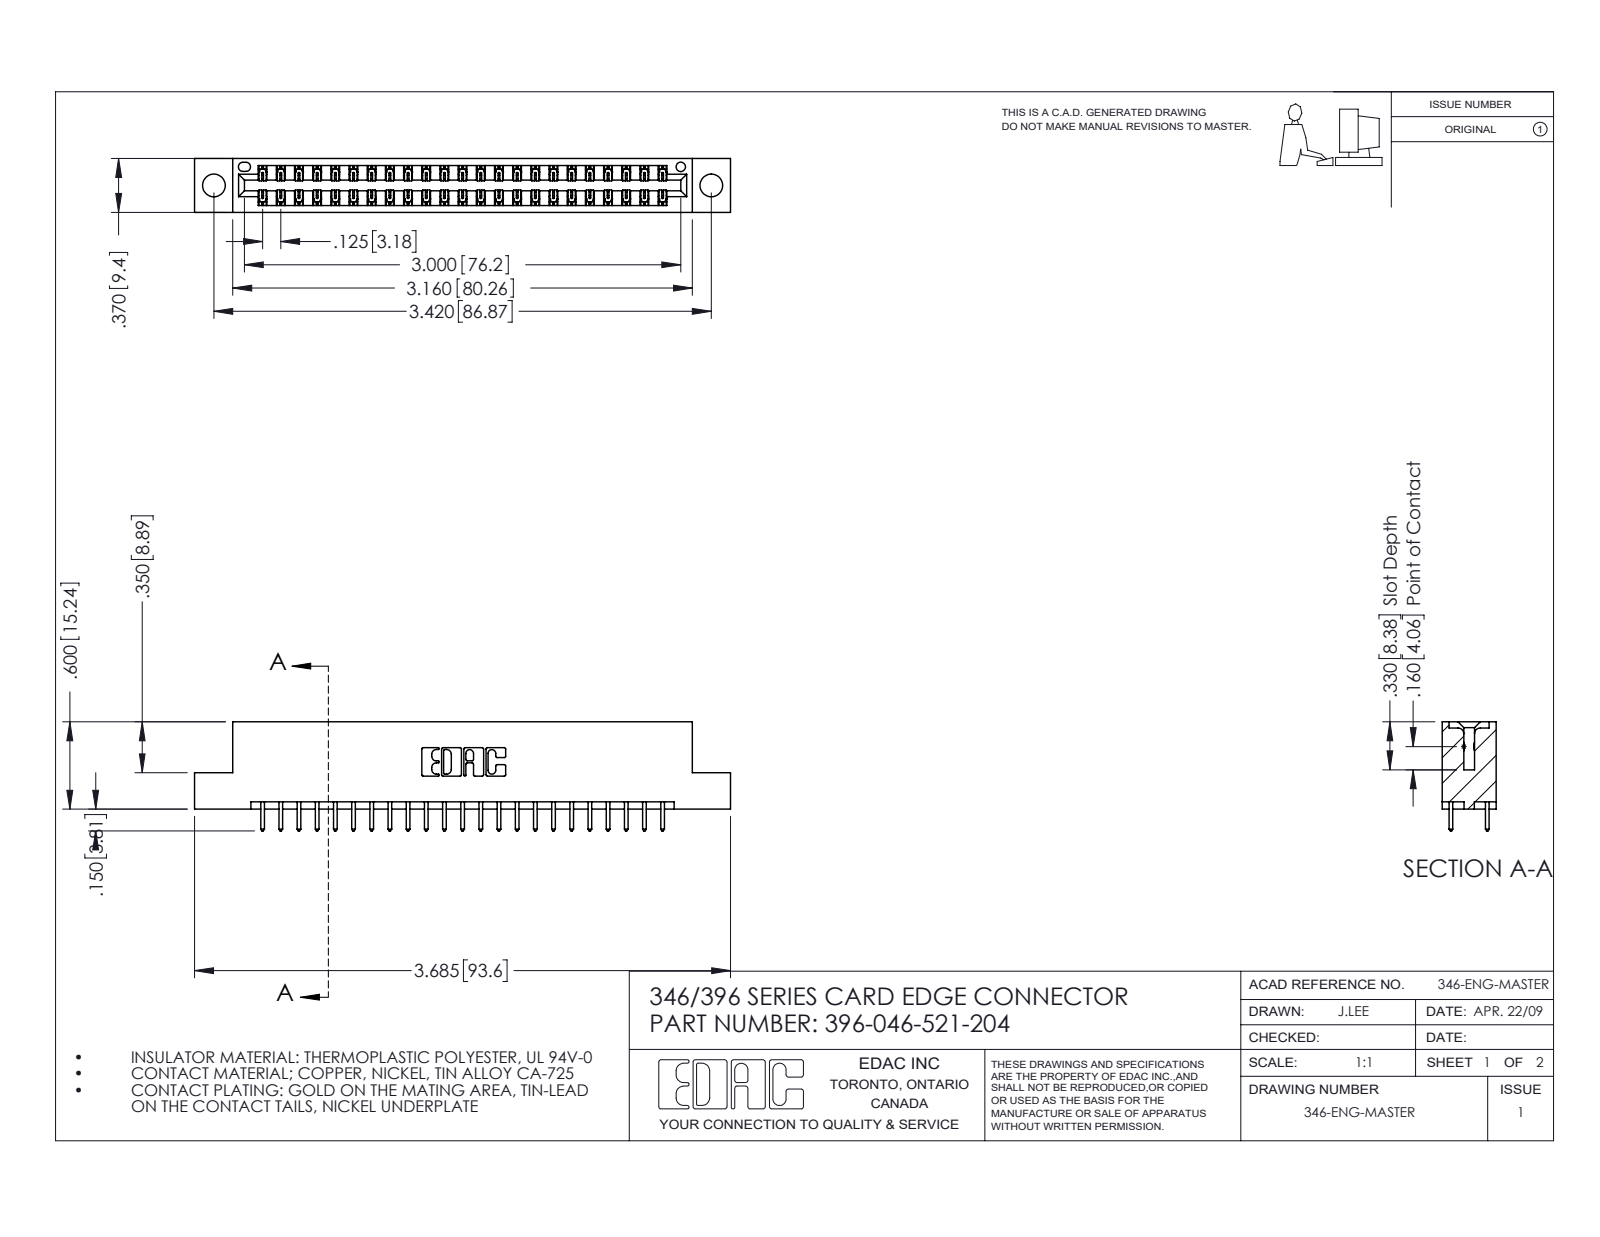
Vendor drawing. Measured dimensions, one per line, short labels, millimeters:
name: 345-292-001_345-293-121; 396-046-521-204; 346 Part_Flush Mounting Lugs - 0.156 Dia-TH
written by: SolidWorks 2016 (CONFIG_CONTROL_DESIGN)
unit: mm
bodies: 47 solids, 2514 faces (1686 planar, 828 cylindrical, 0 other)
size: 93.6 × 19.1 × 9.4
volume: 8 870 mm³; area: 11 590 mm²
holes: 2× ⌀4, 1× ⌀1.6
rounds: 69× R0.2, 46× R0.3, 22× R0.3, 6× R0.2, 6× R0.8, 3× R0.7, 2× R0.4, 2× R0.6
face distances: 1.2, 8.2, 6.4, 9.4, 1.8, 7.6, 0.6, 7, 3.8, 5.6
hole spacings: 6.2, 81.6, 86.9
